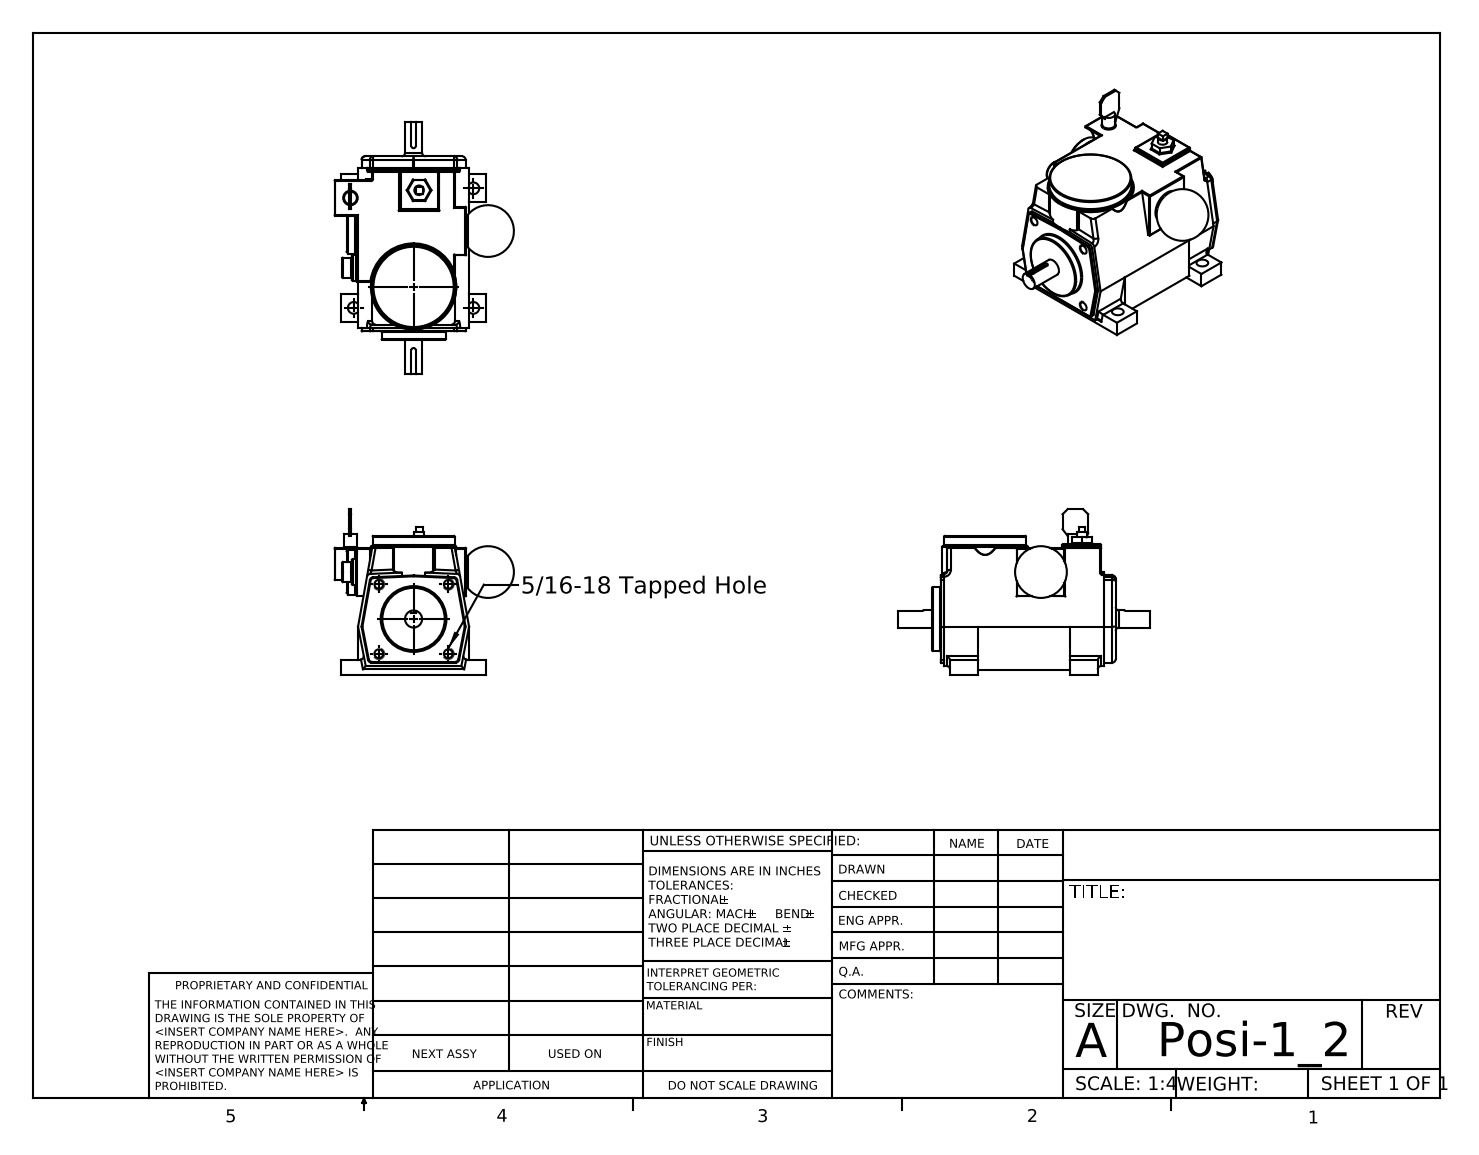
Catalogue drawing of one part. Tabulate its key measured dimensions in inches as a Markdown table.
| quantity | value |
| --- | --- |
| part name | Posi-1_2 |
| STEP written by | SolidWorks 2010 (CONFIG_CONTROL_DESIGN) |
| units | inches |
| bodies | 1 solid, 312 faces (111 planar, 127 cylindrical, 74 other) |
| overall size | 7.375 × 5.25 × 4.841 |
| volume | 60.7 in³ |
| surface area | 122.4 in² |
| round holes (diameter × count) | 0.257 × 4, 0.344 × 4 |
| round bosses / shafts (diameter × count) | 2.4 × 1, 1.875 × 1, 1.32 × 1, 0.75 × 1, 0.6 × 1, 0.5 × 1, 0.375 × 1, 0.28 × 1 |
| partial cylindrical surfaces (radius × count) | 0.025 × 48, 0.1 × 27, 0.063 × 2, 0.475 × 1, 0.811 × 1, 1.25 × 1 |
| main face-to-face distances | 0.35, 3.713, 0.125, 3.588, 3.938, 0.1, 4.063, 0.25, 5.125, 3.25 |
| hole center spacings | 3.5, 2.033, 2.033, 2.875, 4.95 |
